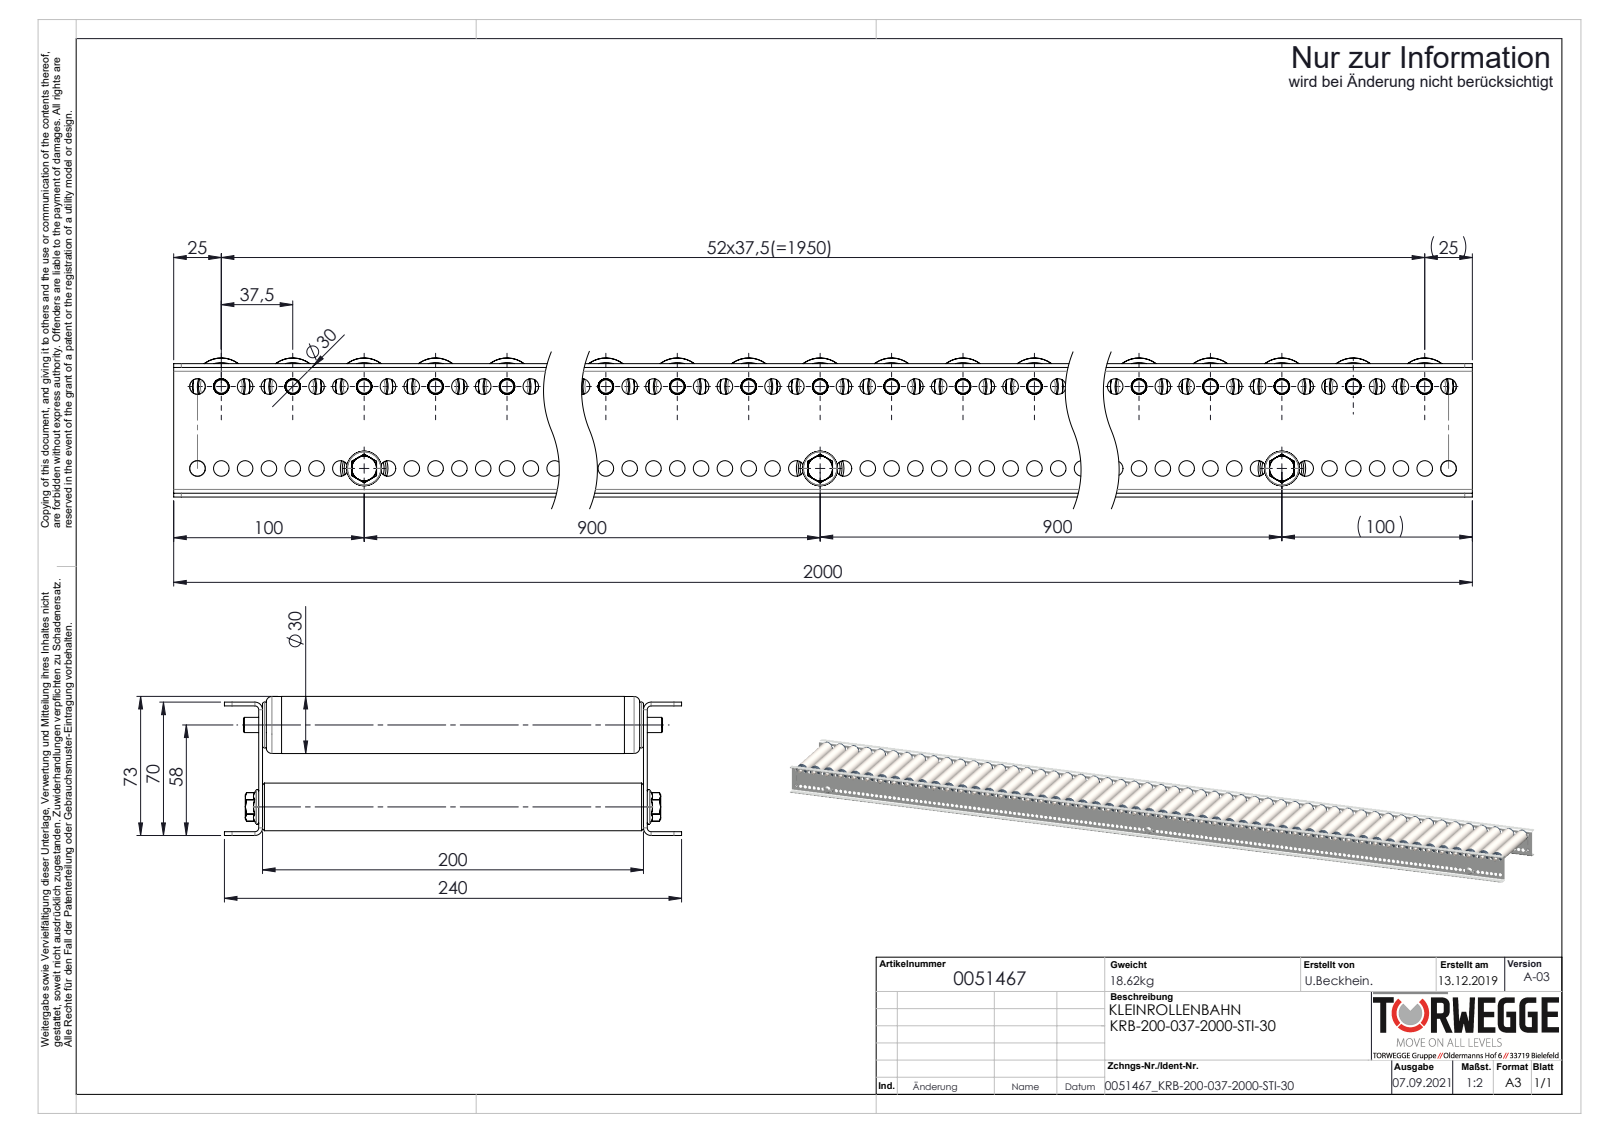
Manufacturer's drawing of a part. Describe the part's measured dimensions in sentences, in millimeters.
The part is named "Traversen_KFG_L200; S100994_Sperrzahnschraube_M08x16-8.8-A2K; 0051467; 0039768_Tragrollenrohr-Ø30x1,5STI_KFG_0039768_L=180 (+6 more)". Its 3-D file was written by "SolidWorks 2020 (AUTOMOTIVE_DESIGN)". It is 335 solids with 14068 faces: 4402 planar, 5588 cylindrical and 4078 other. Overall it measures 2000 by 240 by 73 millimeters. Its volume is 2 788 000 cubic millimeters and its surface area 3 682 000 square millimeters. Round holes: 318 of diameter 8.2, 53 of diameter 8, 53 of diameter 8.1, 53 of diameter 23.2, 53 of diameter 25.2, 53 of diameter 27, 3 of diameter 6.8, 3 of diameter 21. Round bosses or shafts: 53 of diameter 30, 53 of diameter 29.9, 53 of diameter 27.1, 53 of diameter 26.8, 53 of diameter 24, 53 of diameter 14, 3 of diameter 25, 3 of diameter 8. Partial cylindrical surfaces (rounded edges, fillets, slot ends): 53 of radius 5.05, 8 of radius 4, 4 of radius 2. The main face-to-face distances are 2, 202, 200, 68, 204, 70, 66, 10, 190, 20. The hole center spacings are 12.5, 25, 37.5, 50, 62.5, 75, 87.5, 100.
